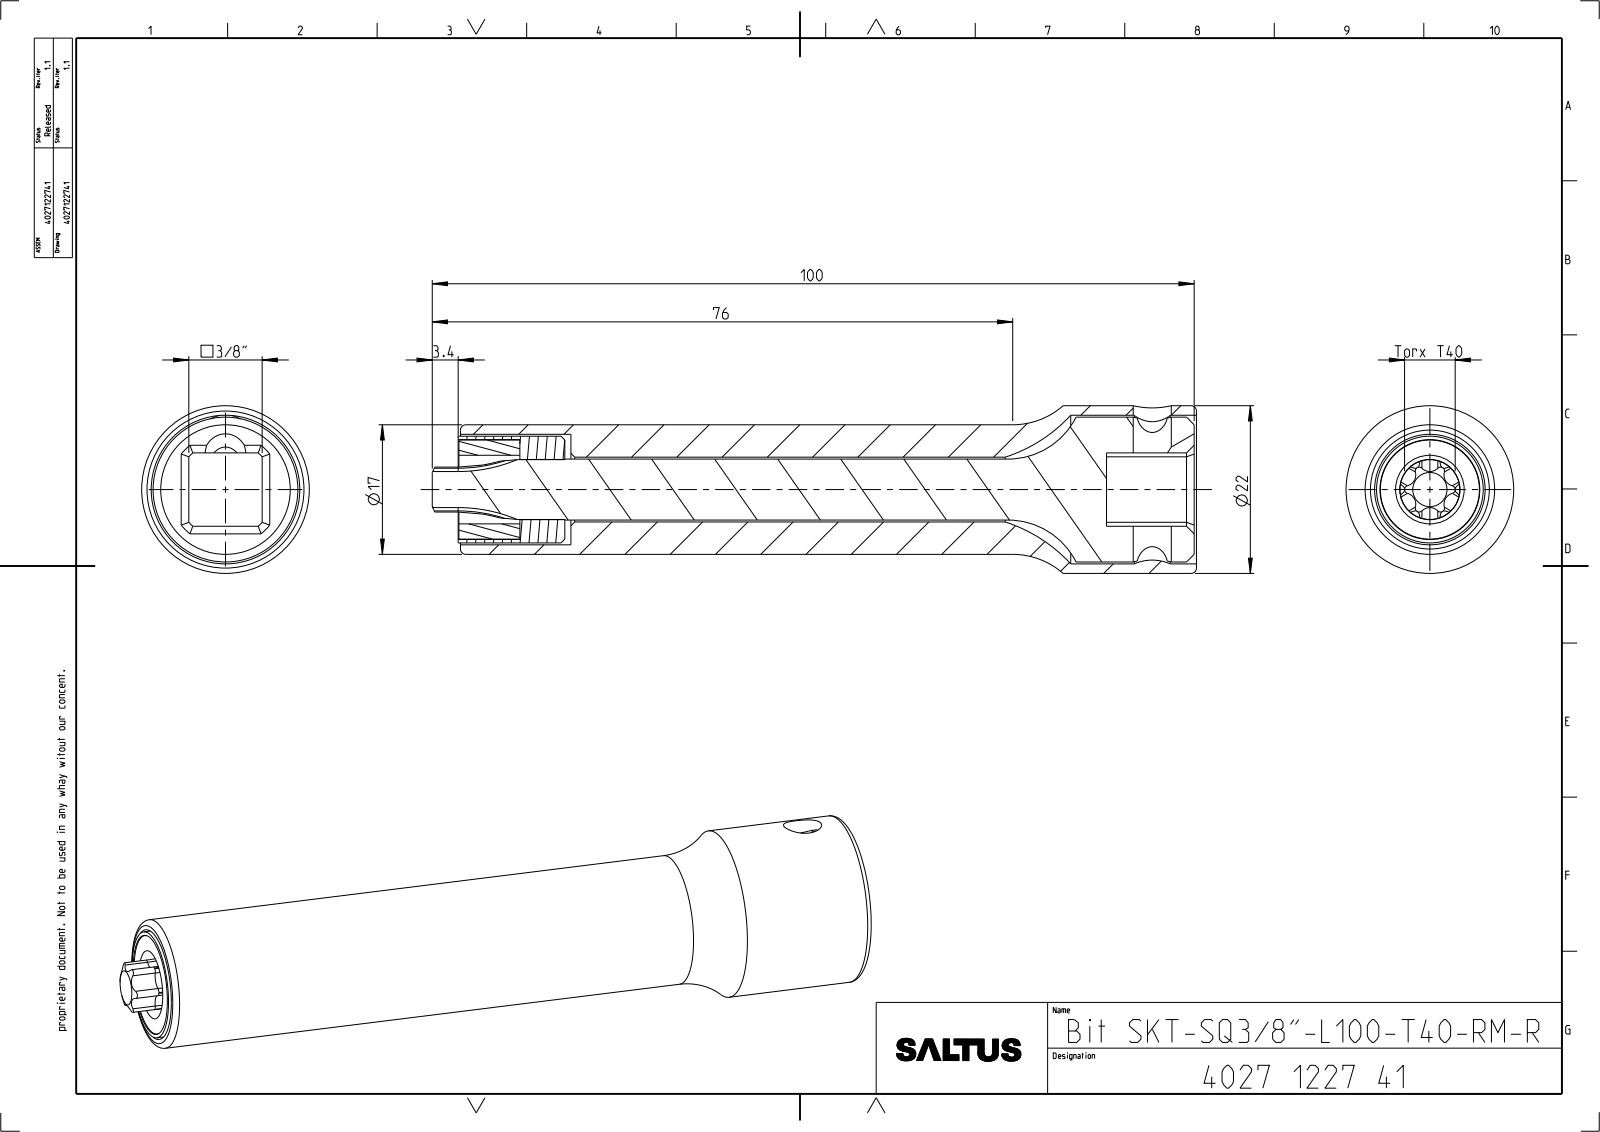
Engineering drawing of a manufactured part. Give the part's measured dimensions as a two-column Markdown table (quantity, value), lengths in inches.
| quantity | value |
| --- | --- |
| part name | 4027905843; 4027901682; 4027907743; 4027904092_ASM (+2 more) |
| STEP written by | CREO PARAMETRIC BY PTC INC, 2022414 (CONFIG_CONTROL_DESIGN) |
| units | inches |
| bodies | 4 solids, 129 faces (21 planar, 59 cylindrical, 49 other) |
| overall size | 3.949 × 0.866 × 0.866 |
| volume | 1.334 in³ |
| surface area | 23.67 in² |
| round holes (diameter × count) | 0.197 × 1, 0.311 × 1, 0.335 × 1, 0.354 × 1, 0.516 × 1, 0.571 × 1, 0.768 × 1 |
| round bosses / shafts (diameter × count) | 0.866 × 1, 0.748 × 1, 0.669 × 1, 0.551 × 1, 0.512 × 1, 0.315 × 1, 0.309 × 1 |
| partial cylindrical surfaces (radius × count) | 0.02 × 6, 0.058 × 6, 0.118 × 1, 0.131 × 1, 0.254 × 1 |
| main face-to-face distances | 0.379, 0.453, 3.484, 0.264, 2.768, 3.031, 3.22, 3.252, 2.799, 0.031 |
